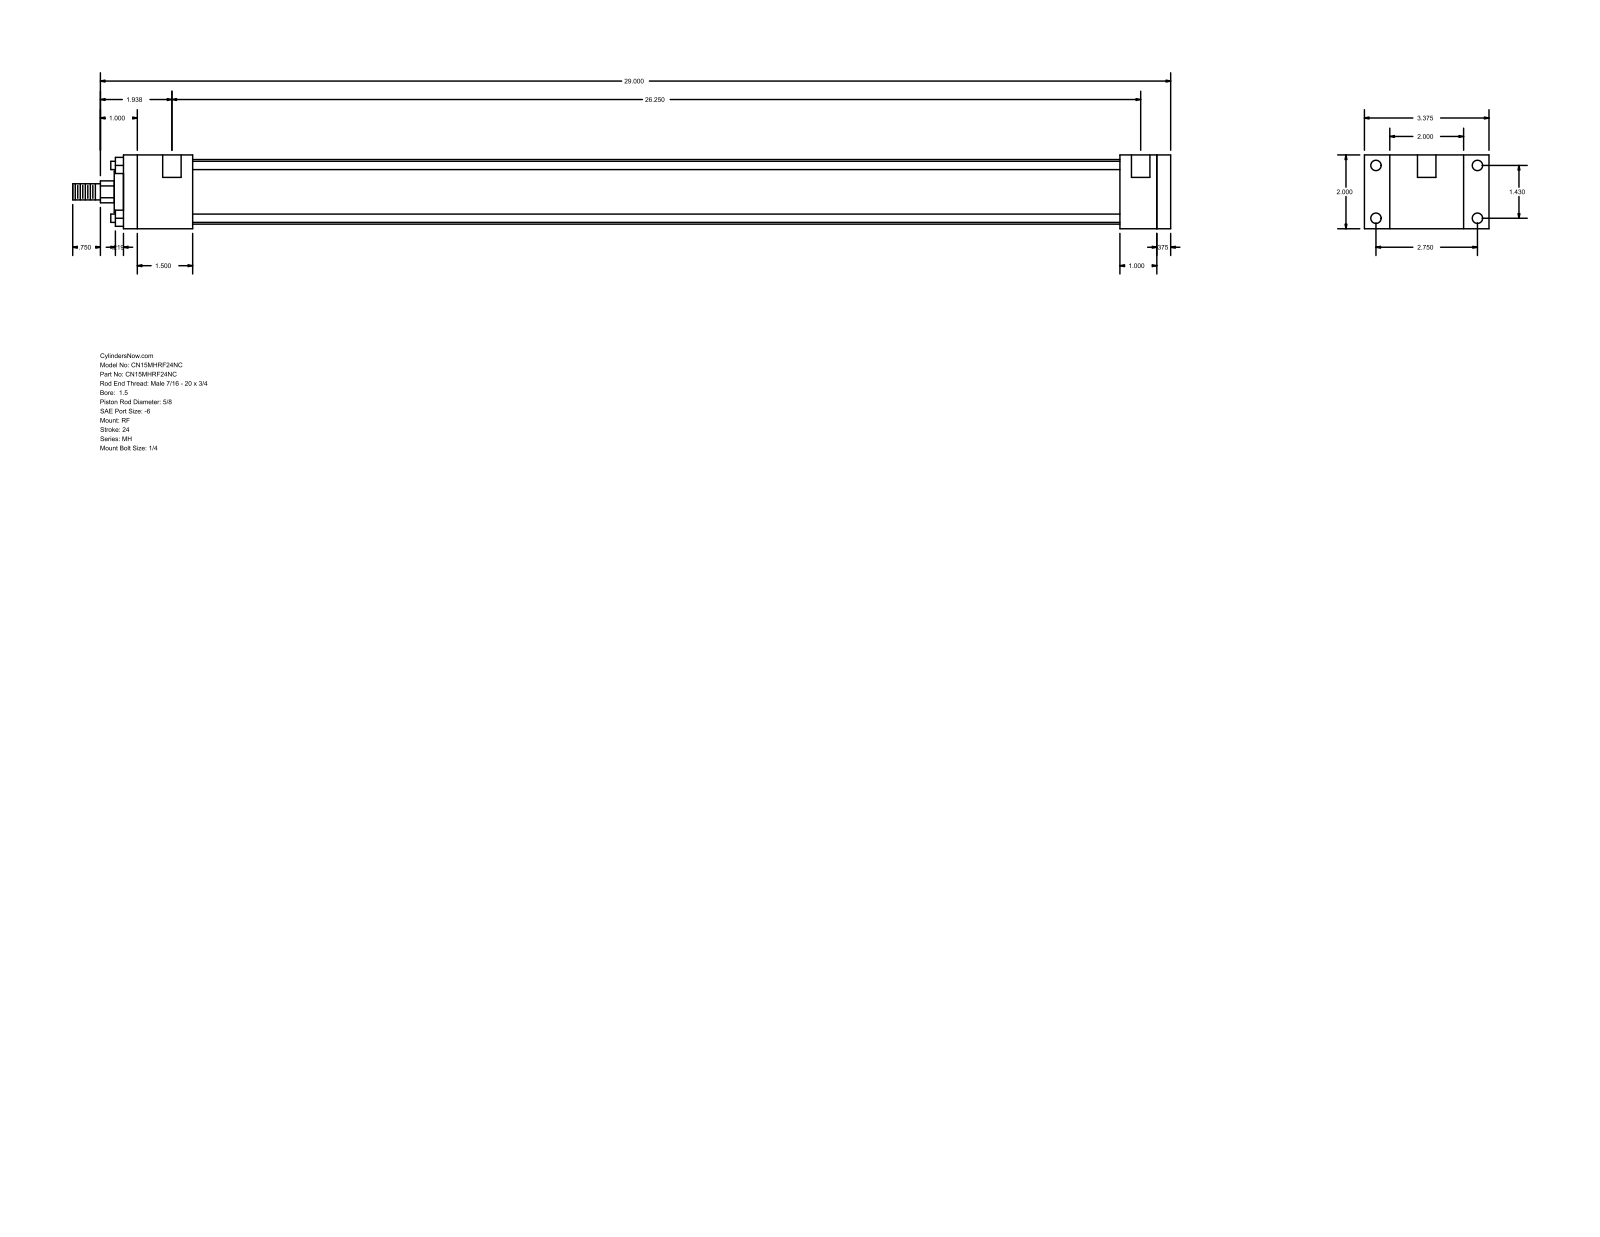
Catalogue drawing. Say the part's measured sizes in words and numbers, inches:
The part is named "MH_RF__0150_0.625". Its 3-D file was written by "GSSL Pune (CONFIG_CONTROL_DESIGN)". It is 0 solids with 92 faces: 64 planar, 28 cylindrical and 0 other. Overall it measures 29.75 by 3.375 by 2 inches. Round holes: 4 of diameter 0.219, 4 of diameter 0.281, 2 of diameter 0.5. Round bosses or shafts: 4 of diameter 0.225, 1 of diameter 1.75, 1 of diameter 1.125, 1 of diameter 0.625, 1 of diameter 0.437. Partial cylindrical surfaces (rounded edges, fillets, slot ends): 1 of radius 0.297. The main face-to-face distances are 2, 0.375, 28.375, 28, 1.375, 0.687, 2.687, 27, 1, 1.875. The hole center spacings are 1.43, 2.75, 3.099, 26.375, 0.125, 26.25.
